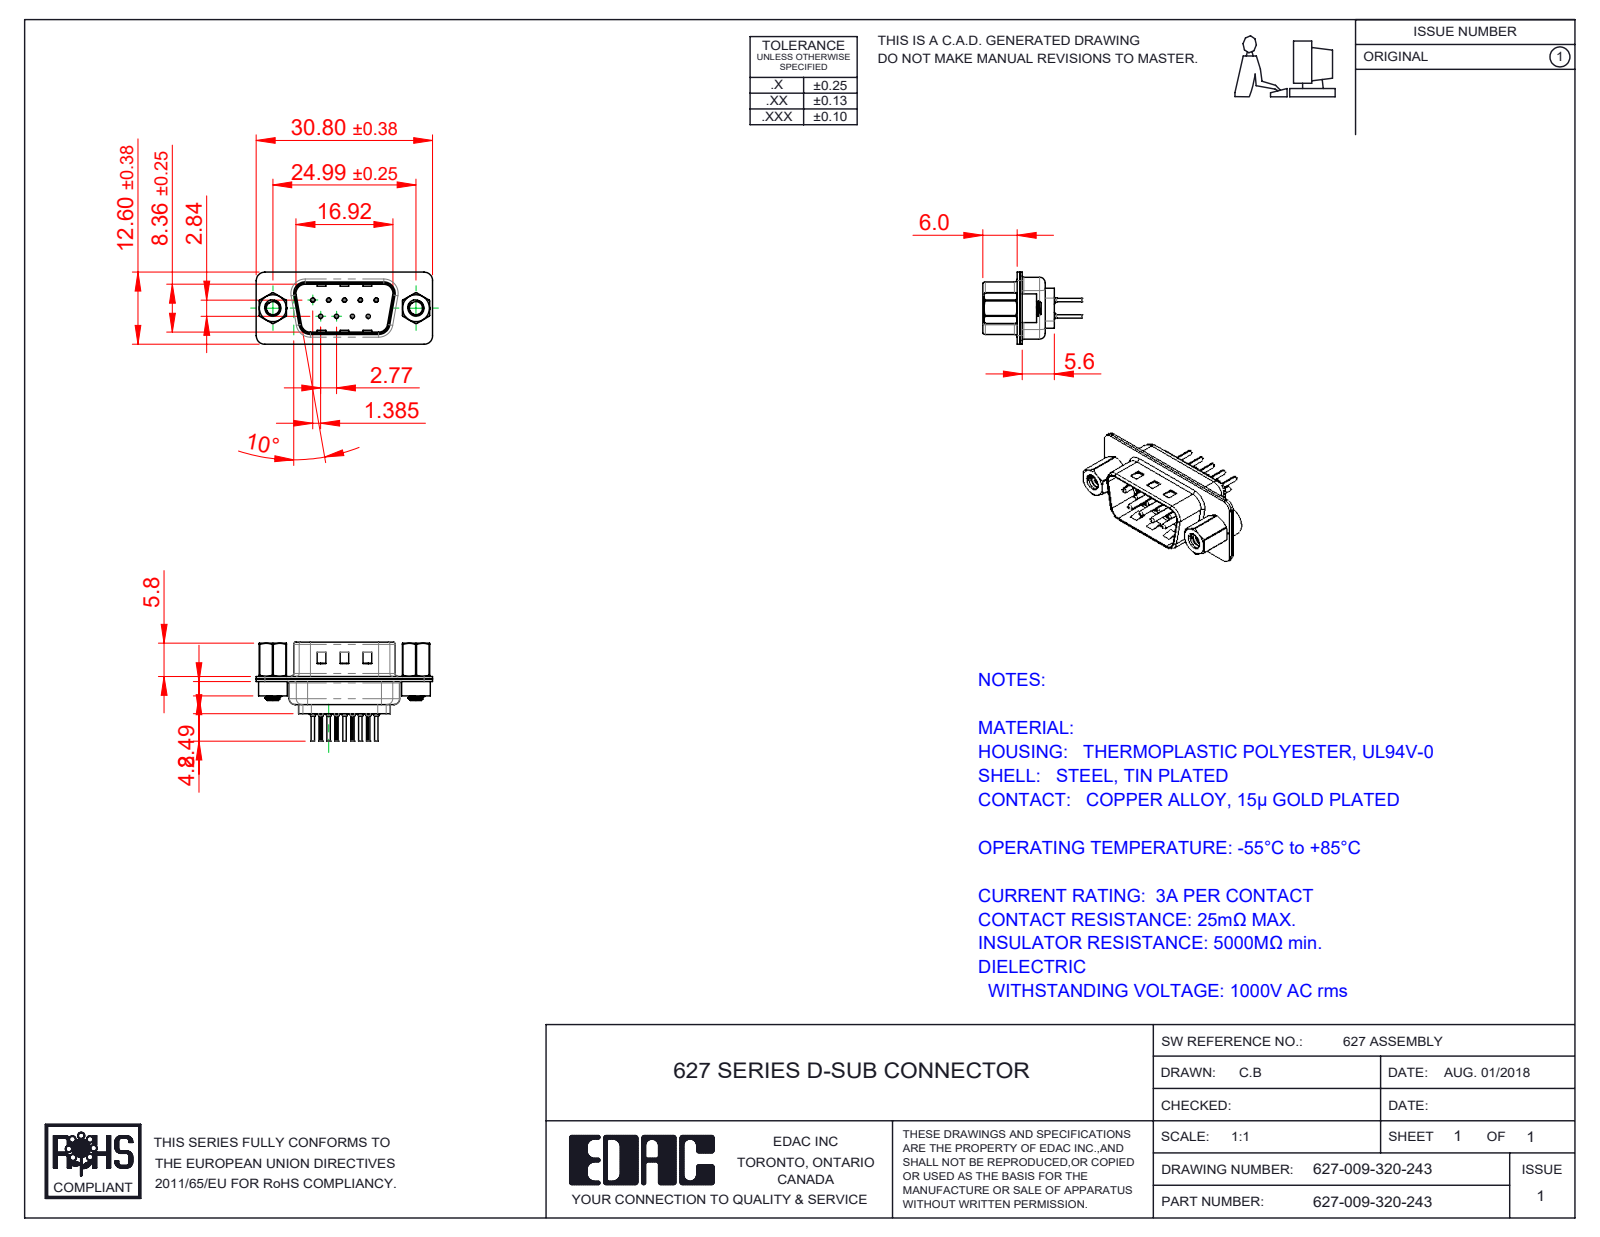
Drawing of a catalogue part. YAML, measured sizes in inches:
part_name: "627 4-40 Threaded Rivet; 627 Contact Row 1_20L; 627 Shell Front_09 Contacts; 627-009-320-243 (+4 more)"
step_written_by: "SolidWorks 2020 (CONFIG_CONTROL_DESIGN)"
units: inches
bodies: {solids: 16, faces: 1308, planar: 345, cylindrical: 532, other: 431}
overall_size: [1.213, 0.681, 0.496]
volume: 0.093
surface_area: 6.829
round_holes:
  - {diameter: 0.008, count: 9}
  - {diameter: 0.014, count: 9}
  - {diameter: 0.043, count: 9}
  - {diameter: 0.063, count: 9}
  - {diameter: 0.089, count: 2}
  - {diameter: 0.09, count: 2}
  - {diameter: 0.157, count: 2}
  - {diameter: 0.189, count: 2}
round_bosses_or_shafts:
  - {diameter: 0.079, count: 9}
  - {diameter: 0.059, count: 9}
  - {diameter: 0.03, count: 9}
  - {diameter: 0.024, count: 9}
  - {diameter: 0.197, count: 2}
  - {diameter: 0.193, count: 2}
  - {diameter: 0.11, count: 2}
partial_cylinders:
  - {radius: 0.004, count: 18}
  - {radius: 0.059, count: 18}
  - {radius: 0.079, count: 12}
  - {radius: 0.02, count: 8}
  - {radius: 0.063, count: 8}
  - {radius: 0.01, count: 4}
  - {radius: 0.024, count: 4}
  - {radius: 0.026, count: 4}
face_to_face_distances: [0.018, 0.016, 0.035, 0.032, 0.377, 0.055, 0.345, 0.02, 0.059, 0.22]
hole_center_spacings: [0.124, 0.109, 0.218, 0.198, 0.198, 0.327, 0.294, 0.295]
